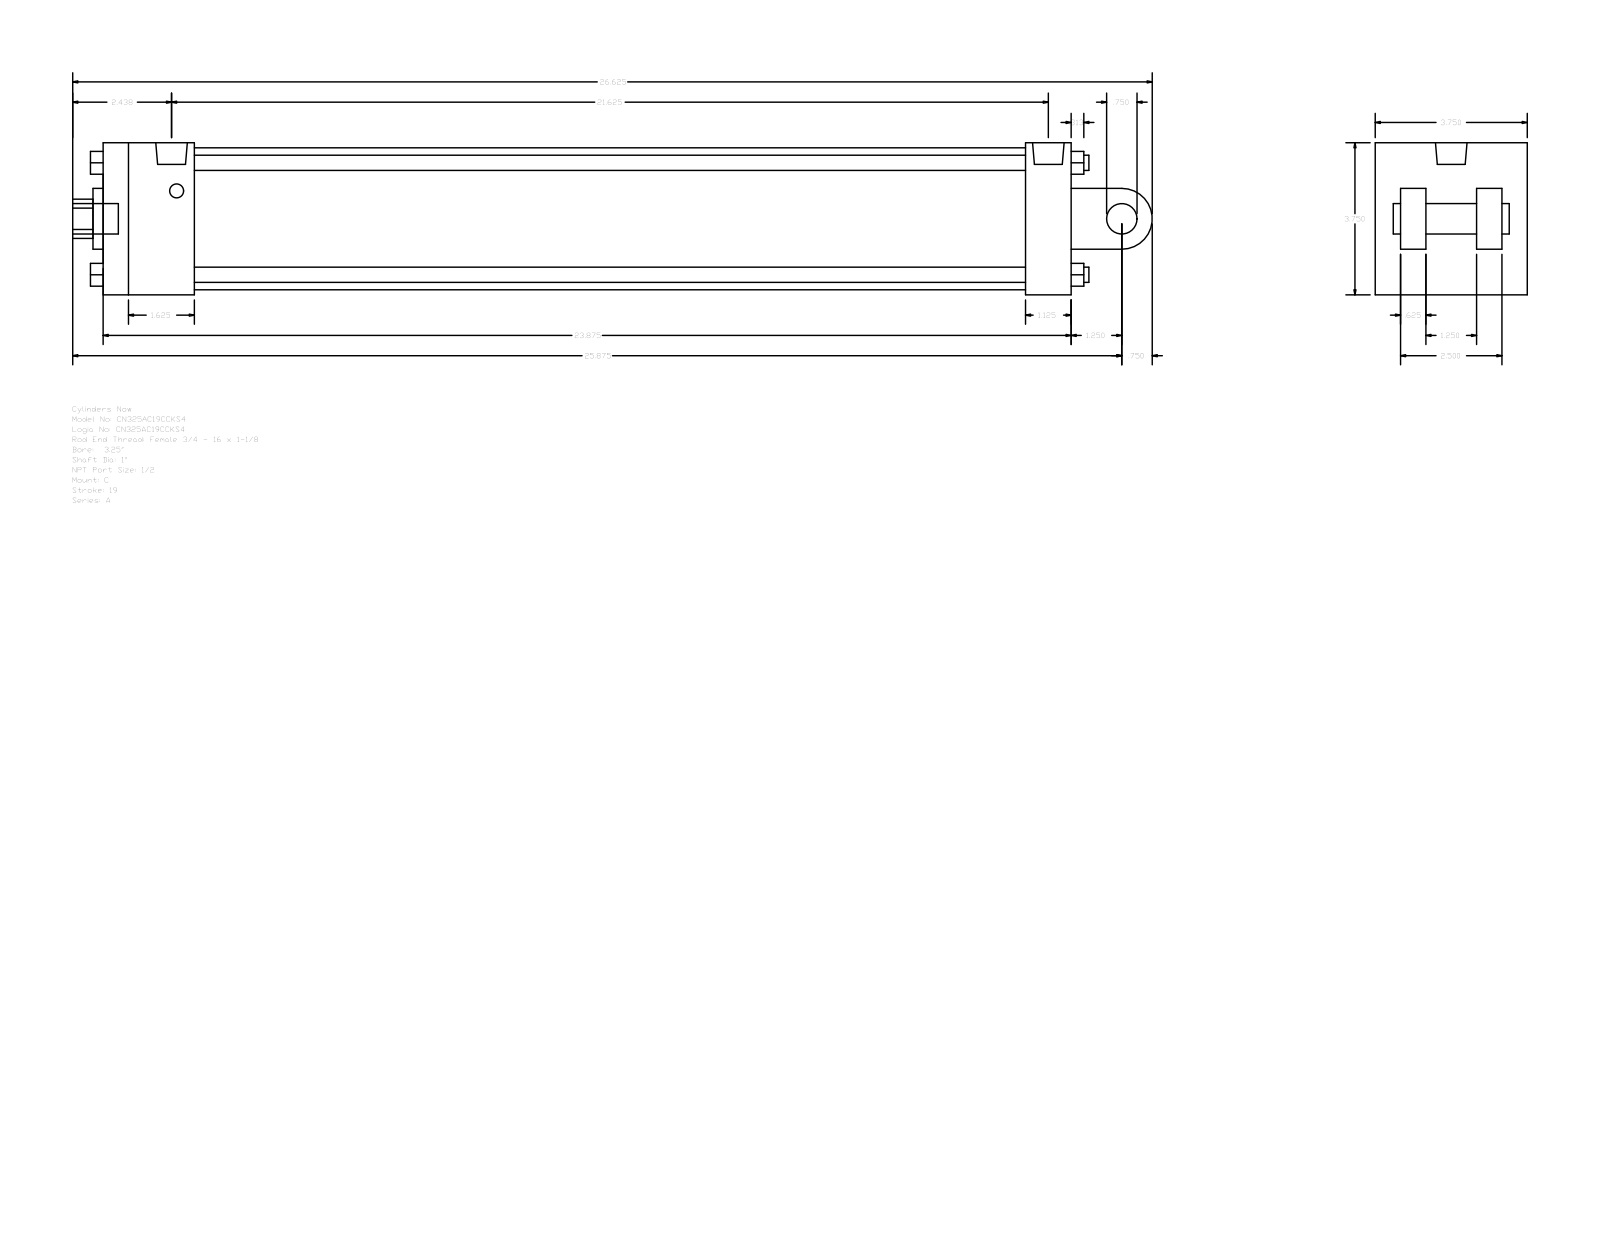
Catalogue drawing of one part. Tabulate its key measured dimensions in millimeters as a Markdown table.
| quantity | value |
| --- | --- |
| part name | A_C__0325_1 |
| STEP written by | GSSL Pune (CONFIG_CONTROL_DESIGN) |
| units | millimeters |
| bodies | 0 solids, 135 faces (102 planar, 33 cylindrical, 0 other) |
| overall size | 676.27 × 95.25 × 95.25 |
| round holes (diameter × count) | 8.73 × 2, 19.77 × 1, 25.4 × 1, 38.1 × 1, 88.9 × 1 |
| round bosses / shafts (diameter × count) | 9.53 × 4, 19.05 × 2, 8.73 × 2, 19.77 × 1 |
| partial cylindrical surfaces (radius × count) | 12.29 × 1, 19.05 × 1 |
| main face-to-face distances | 95.24, 606.43, 15.87, 63.5, 47.63, 31.74, 79.37, 66.67, 577.85, 28.58 |
| hole center spacings | 3.18 |
